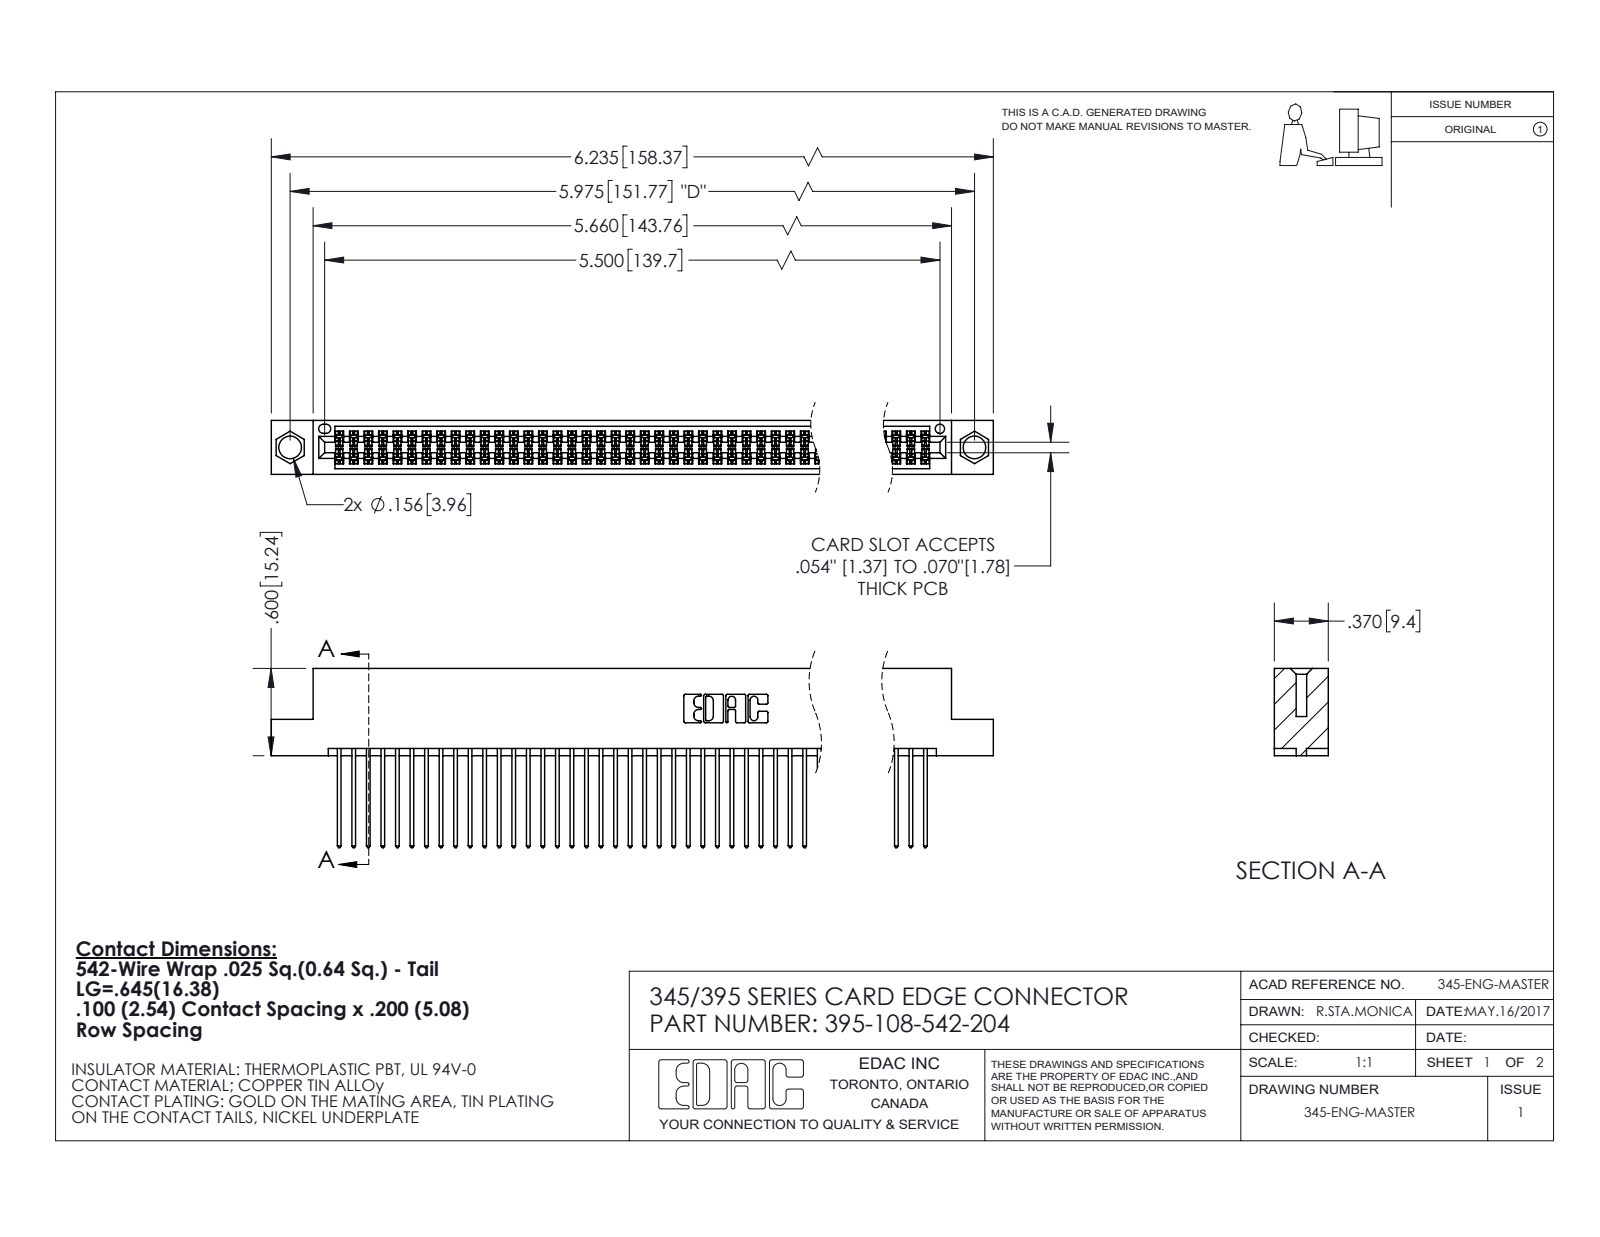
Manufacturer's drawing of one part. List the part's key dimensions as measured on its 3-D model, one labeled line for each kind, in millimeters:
Part name (STEP PRODUCT): 395-108-542-204; 345-292-001_345-293-142; 345 Part_Flush Mounting Lugs - 0.156 Dia-TI
STEP written by: SolidWorks 2020 (CONFIG_CONTROL_DESIGN)
Units: millimetres
Bodies: 109 solids, 5540 faces (3658 planar, 1882 cylindrical, 0 other)
Overall size (bounding box): 158.4 × 31.3 × 9.4
Volume: 15 900 mm³ · Surface area: 25 930 mm²
Round holes (diameter × count): ⌀4 ×2, ⌀1.6 ×1
Partial cylindrical surfaces — rounded edges, fillets, slot ends (radius × count): R0.2 ×162, R0.3 ×108, R0.3 ×22, R0.2 ×6, R0.8 ×6, R0.7 ×3, R0.4 ×2, R0.5 ×2
Main face-to-face distances: 7.6, 1.8, 5.1, 2.5, 6.9, 0.6, 5.7, 9.4, 4.4, 3.8
Hole centre spacings: 6.9, 145.8, 151.8
